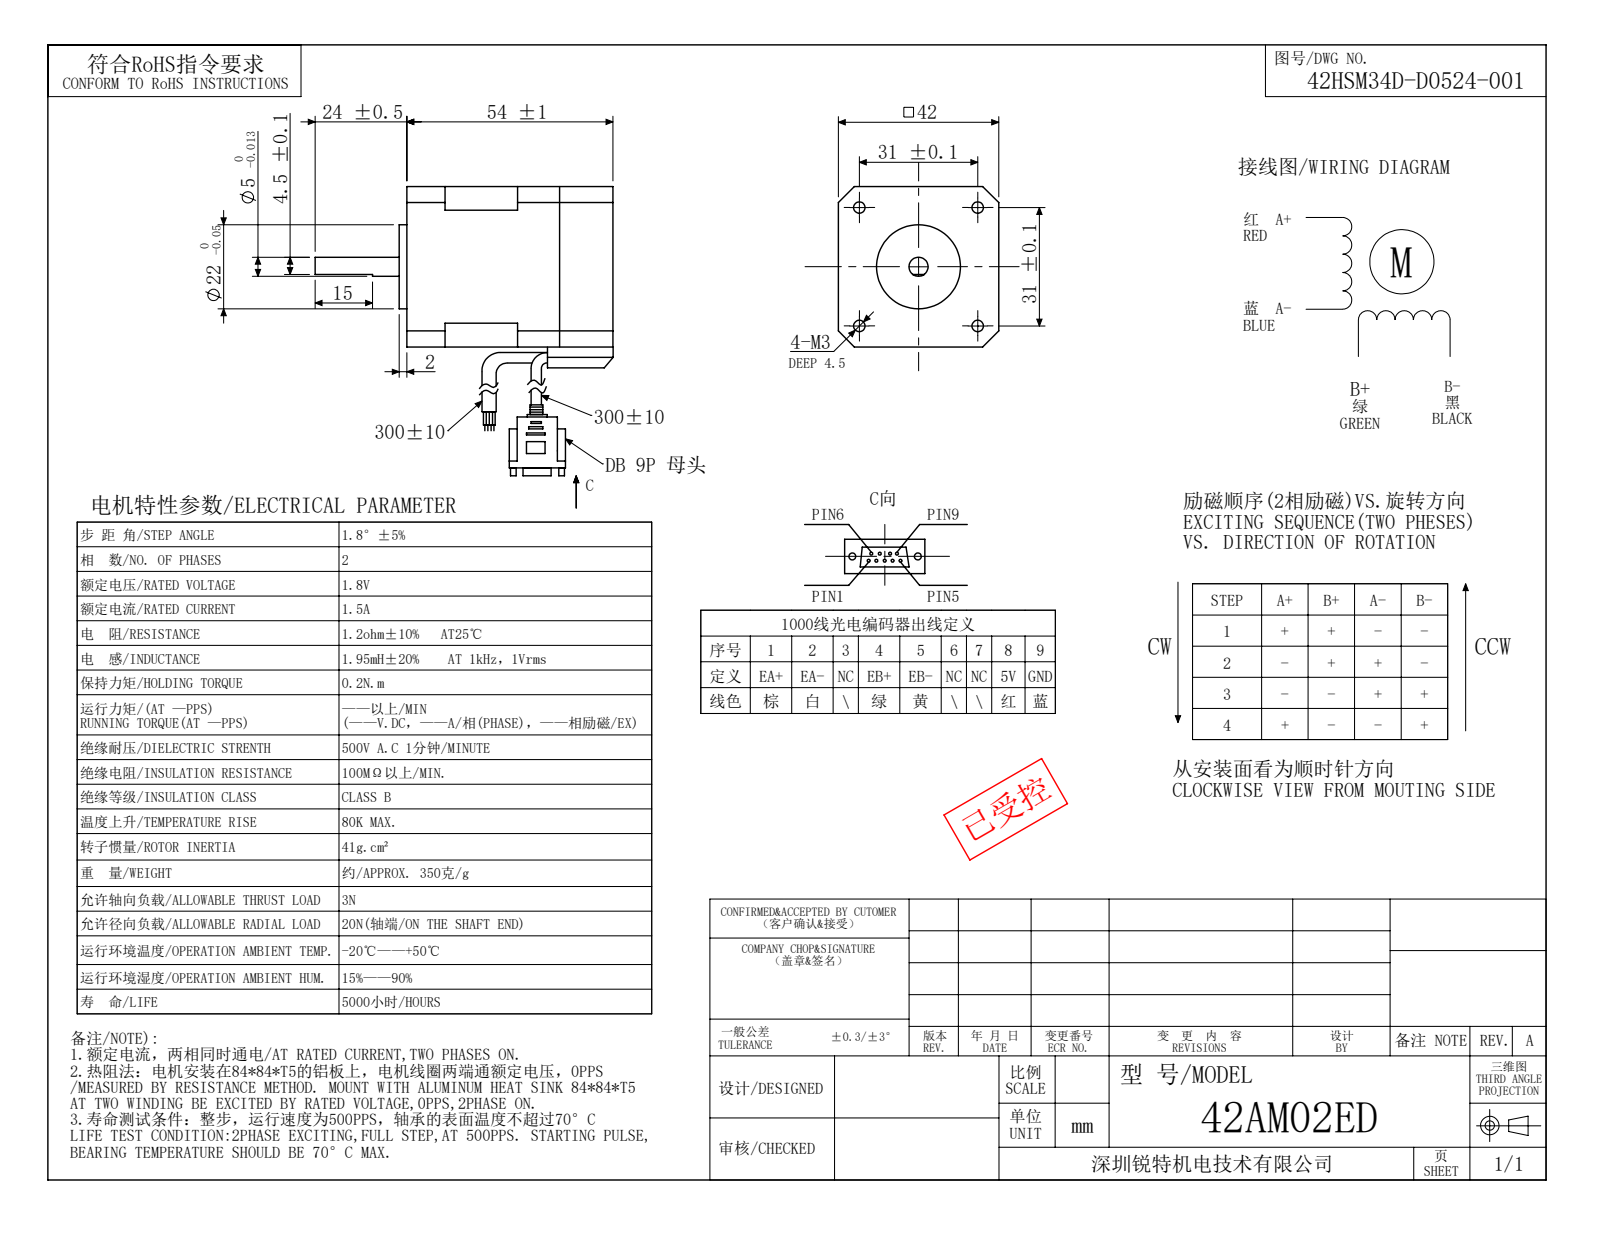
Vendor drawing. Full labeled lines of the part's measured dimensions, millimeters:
Part name (STEP PRODUCT): 42HSM34D-D0524-001
STEP written by: SolidWorks 2023 (AUTOMOTIVE_DESIGN)
Units: millimetres
Bodies: 1 solid, 46 faces (34 planar, 12 cylindrical, 0 other)
Overall size (bounding box): 78 × 42 × 42
Volume: 92 776 mm³ · Surface area: 13 754 mm²
Round holes (diameter × count): ⌀3 ×4
Round bosses / shafts (diameter × count): ⌀22 ×1, ⌀5 ×1
Main face-to-face distances: 42, 54, 1.41, 52.03, 56, 2, 50.62, 53.44, 53.45, 52.04
Hole centre spacings: 31, 43.84
